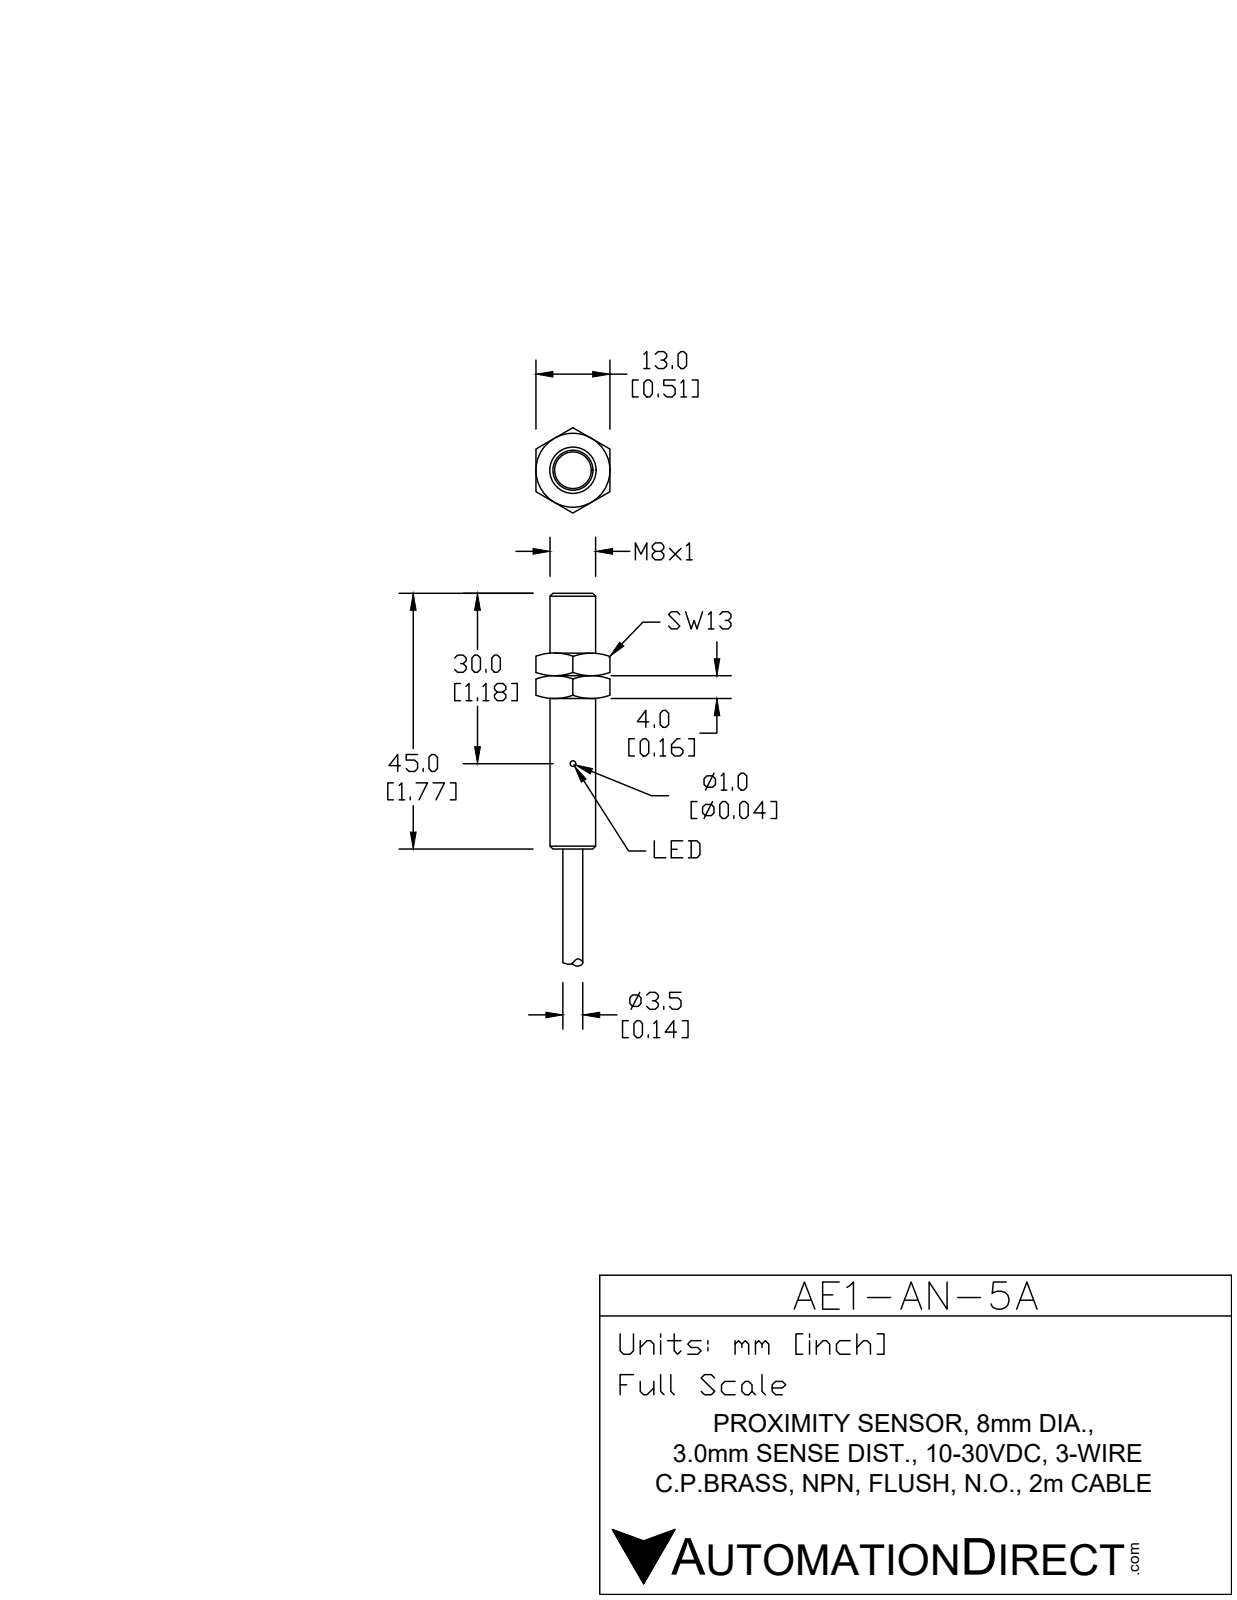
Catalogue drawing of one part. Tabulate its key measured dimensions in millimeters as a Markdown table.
| quantity | value |
| --- | --- |
| part name | AE1-AP-5A |
| STEP written by | SolidWorks 2017 (AUTOMOTIVE_DESIGN) |
| units | millimeters |
| bodies | 1 solid, 10 faces (4 planar, 3 cylindrical, 3 other) |
| overall size | 71.2 × 8 × 8 |
| volume | 2 790 mm³ |
| surface area | 1 632 mm² |
| round bosses / shafts (diameter × count) | 8 × 1, 6.5 × 1, 5 × 1 |
| main face-to-face distances | 71.2, 45.5, 25.7, 45, 0.5, 26.2 |
